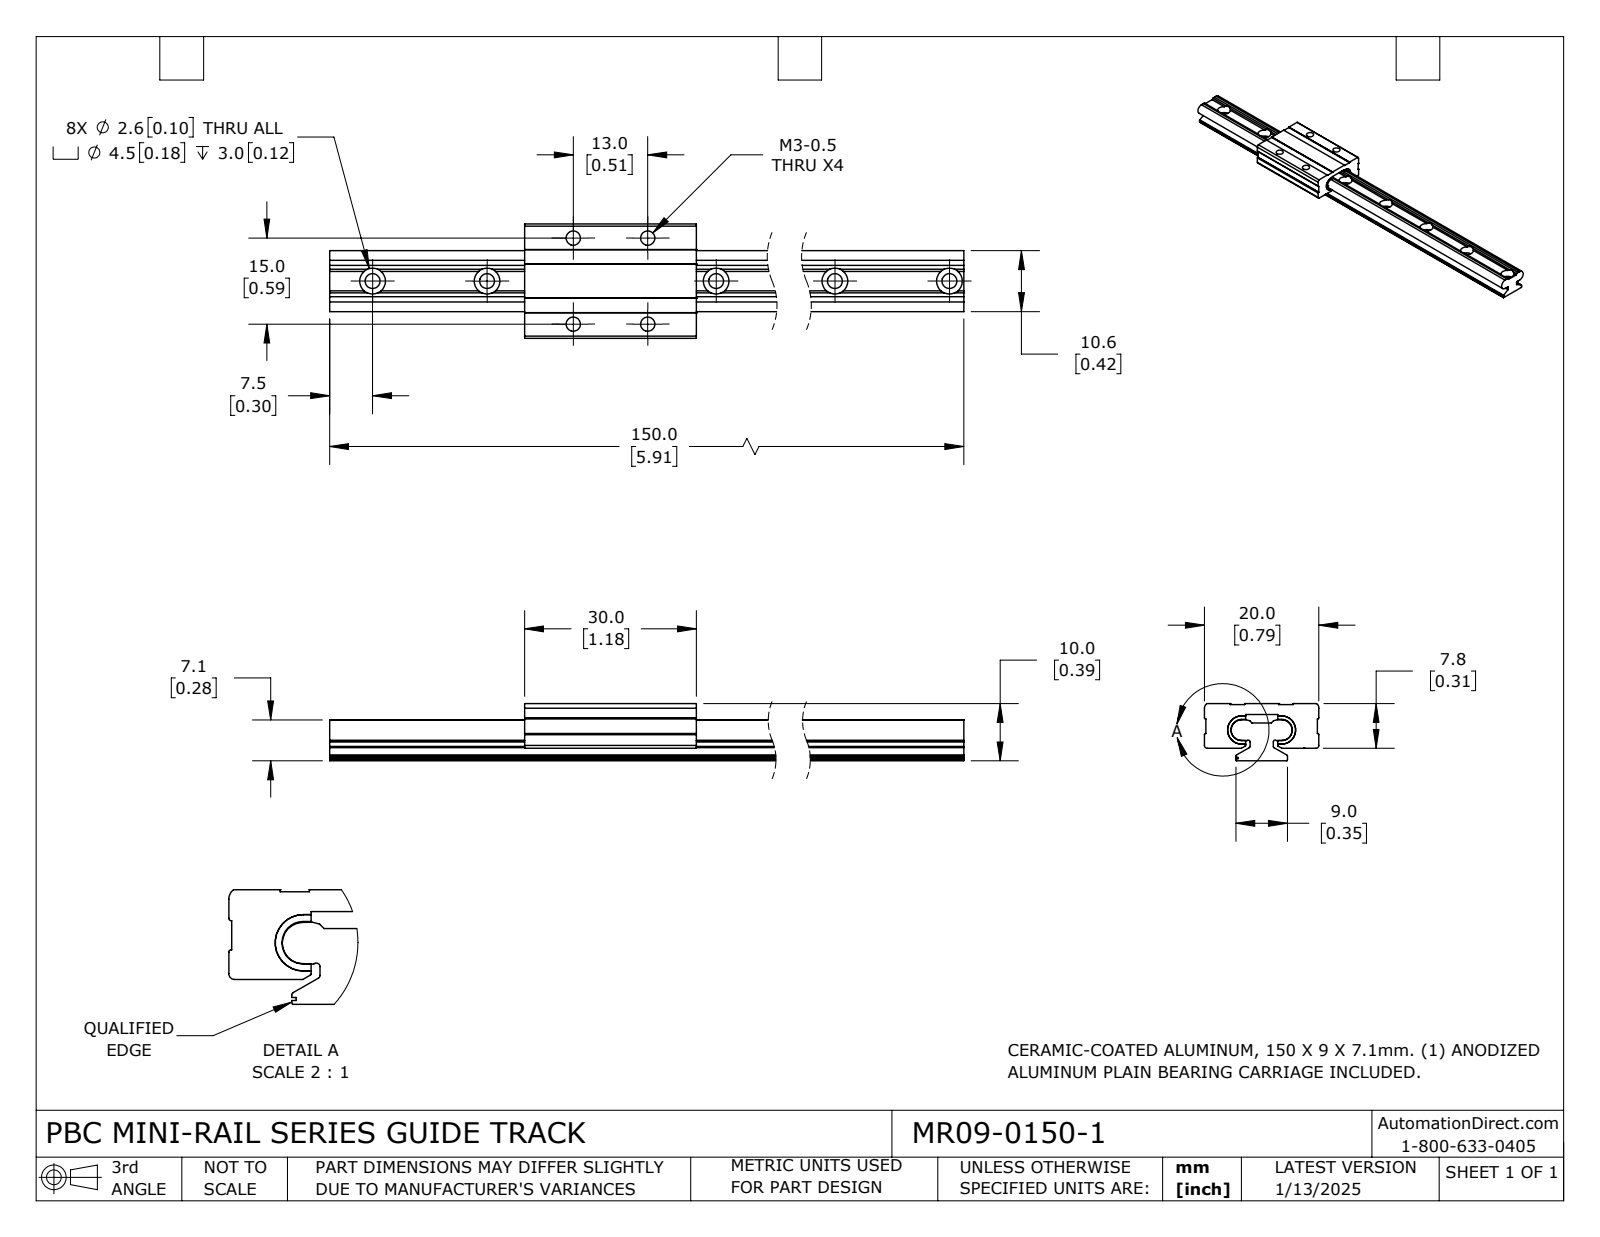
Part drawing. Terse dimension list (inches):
name: MR09-0150-1_CARRIAGE; MR09-0150-1; MR09-0150-1_RAIL
written by: SolidWorks 2023 (CONFIG_CONTROL_DESIGN)
unit: in
bodies: 4 solids, 190 faces (115 planar, 75 cylindrical, 0 other)
size: 5.906 × 0.787 × 0.394
volume: 0.664 in³; area: 16.25 in²
holes: 8× ⌀0.102, 8× ⌀0.177, 4× ⌀0.098
rounds: 10× R0.008, 6× R0.01, 4× R0.073, 2× R0.012, 2× R0.02, 2× R0.04, 2× R0.071, 2× R0.097
face distances: 0.394, 0.261, 0.133, 0.085, 0.175, 0.308, 0.152, 0.313, 0.473, 0.233
hole spacings: 0.787, 1.575, 2.362, 3.15, 3.937, 0.354, 0.433, 0.512
